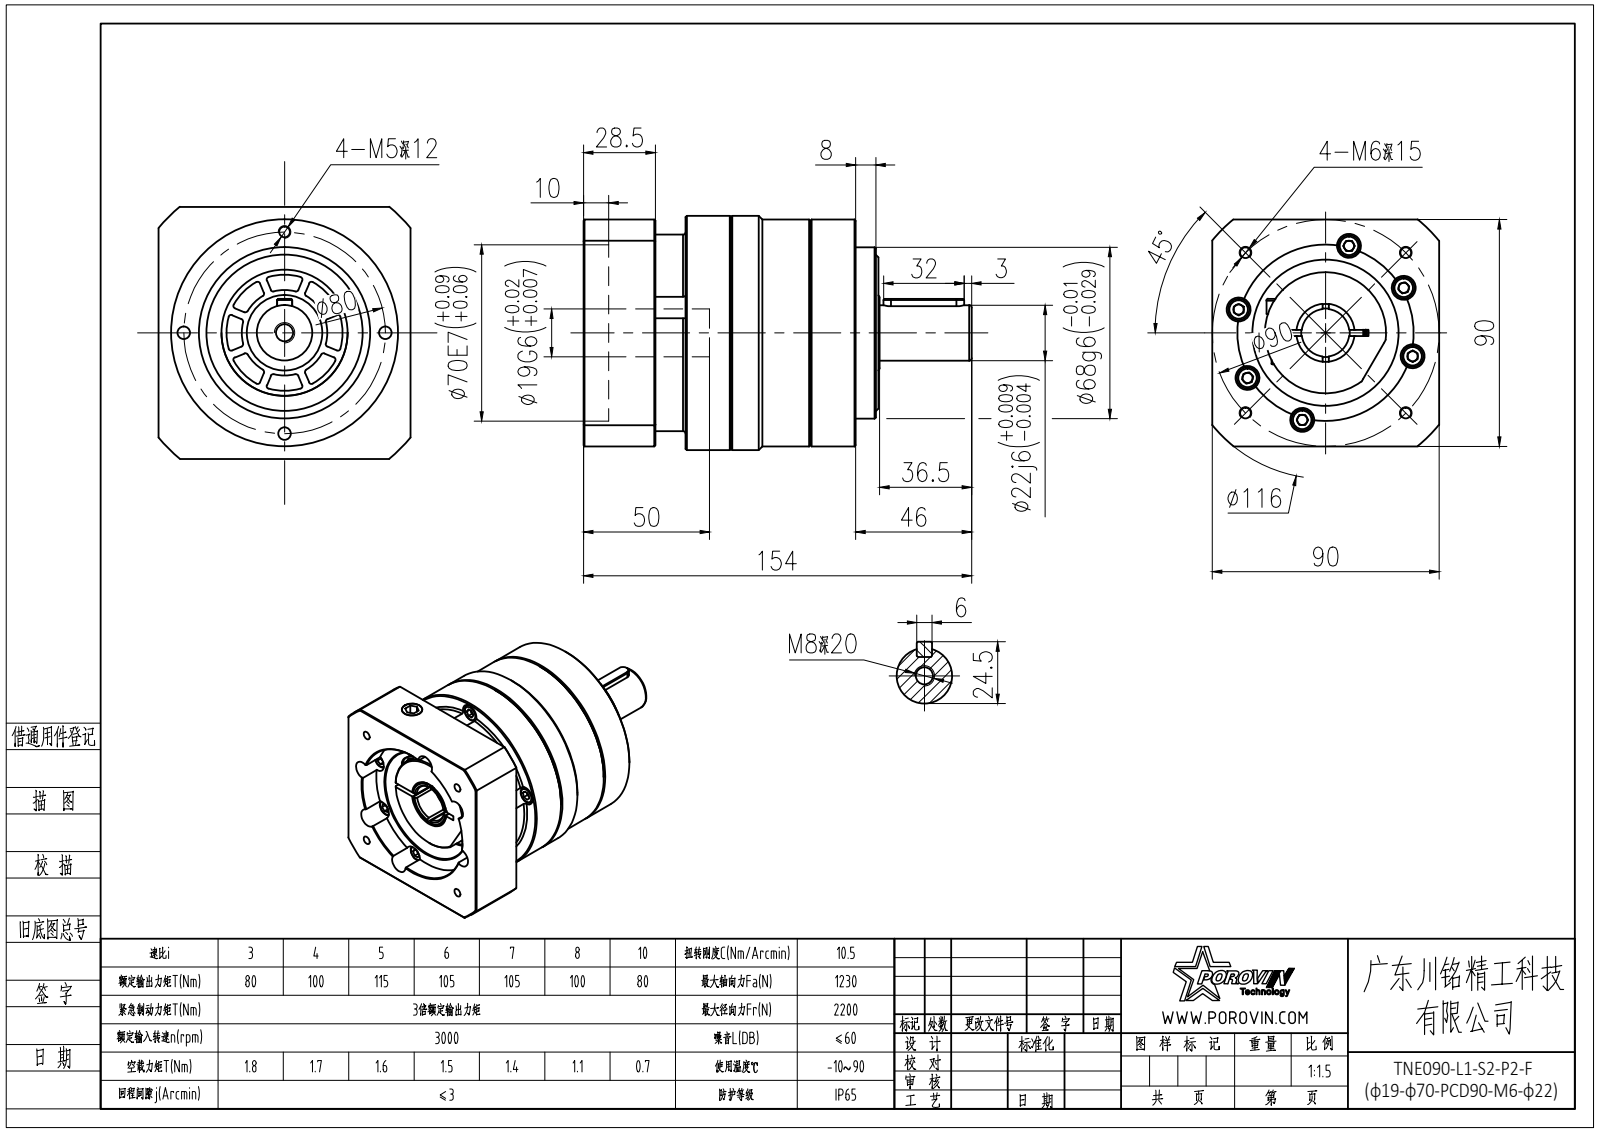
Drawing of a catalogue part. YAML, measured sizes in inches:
part_name: "spring lock washers--normal type gb_GB_FASTENER_WASHER_SW 5; hexagon socket head cap screws gb_GB_FASTENER_SCREWS_HSHCS M5X20-N; 一级齿圈外形图 KE90; hex socket set screws with flat point gb_GB_FASTENER_SCREWS_HSFP M12X12-N (+1 more)"
step_written_by: "SolidWorks 2016 (CONFIG_CONTROL_DESIGN)"
units: inches
bodies: {solids: 29, faces: 842, planar: 335, cylindrical: 315, other: 192}
overall_size: [6.063, 3.661, 3.661]
volume: 39.8
surface_area: 200.3
round_holes:
  - {diameter: 0.213, count: 10}
  - {diameter: 0.217, count: 10}
  - {diameter: 0.374, count: 10}
  - {diameter: 0.197, count: 9}
  - {diameter: 0.165, count: 6}
  - {diameter: 0.256, count: 1}
  - {diameter: 0.268, count: 1}
  - {diameter: 0.335, count: 1}
  - {diameter: 0.402, count: 1}
  - {diameter: 0.748, count: 1}
  - {diameter: 0.756, count: 1}
  - {diameter: 1.969, count: 1}
round_bosses_or_shafts:
  - {diameter: 0.335, count: 10}
  - {diameter: 0.315, count: 10}
  - {diameter: 0.197, count: 10}
  - {diameter: 3.661, count: 1}
  - {diameter: 3.543, count: 1}
  - {diameter: 3.091, count: 1}
  - {diameter: 3.071, count: 1}
  - {diameter: 2.677, count: 1}
partial_cylinders:
  - {radius: 0.039, count: 32}
  - {radius: 0.118, count: 2}
  - {radius: 0.217, count: 1}
  - {radius: 0.906, count: 1}
  - {radius: 1.378, count: 1}
  - {radius: 2.283, count: 1}
face_to_face_distances: [1.24, 3.543, 2.303, 1.28, 2.52, 0.098, 0.709, 1.024, 1.949, 1.122]
hole_center_spacings: [1.293, 3.093, 1.407, 2.986, 0.423, 0.895, 1.301, 1.575]
